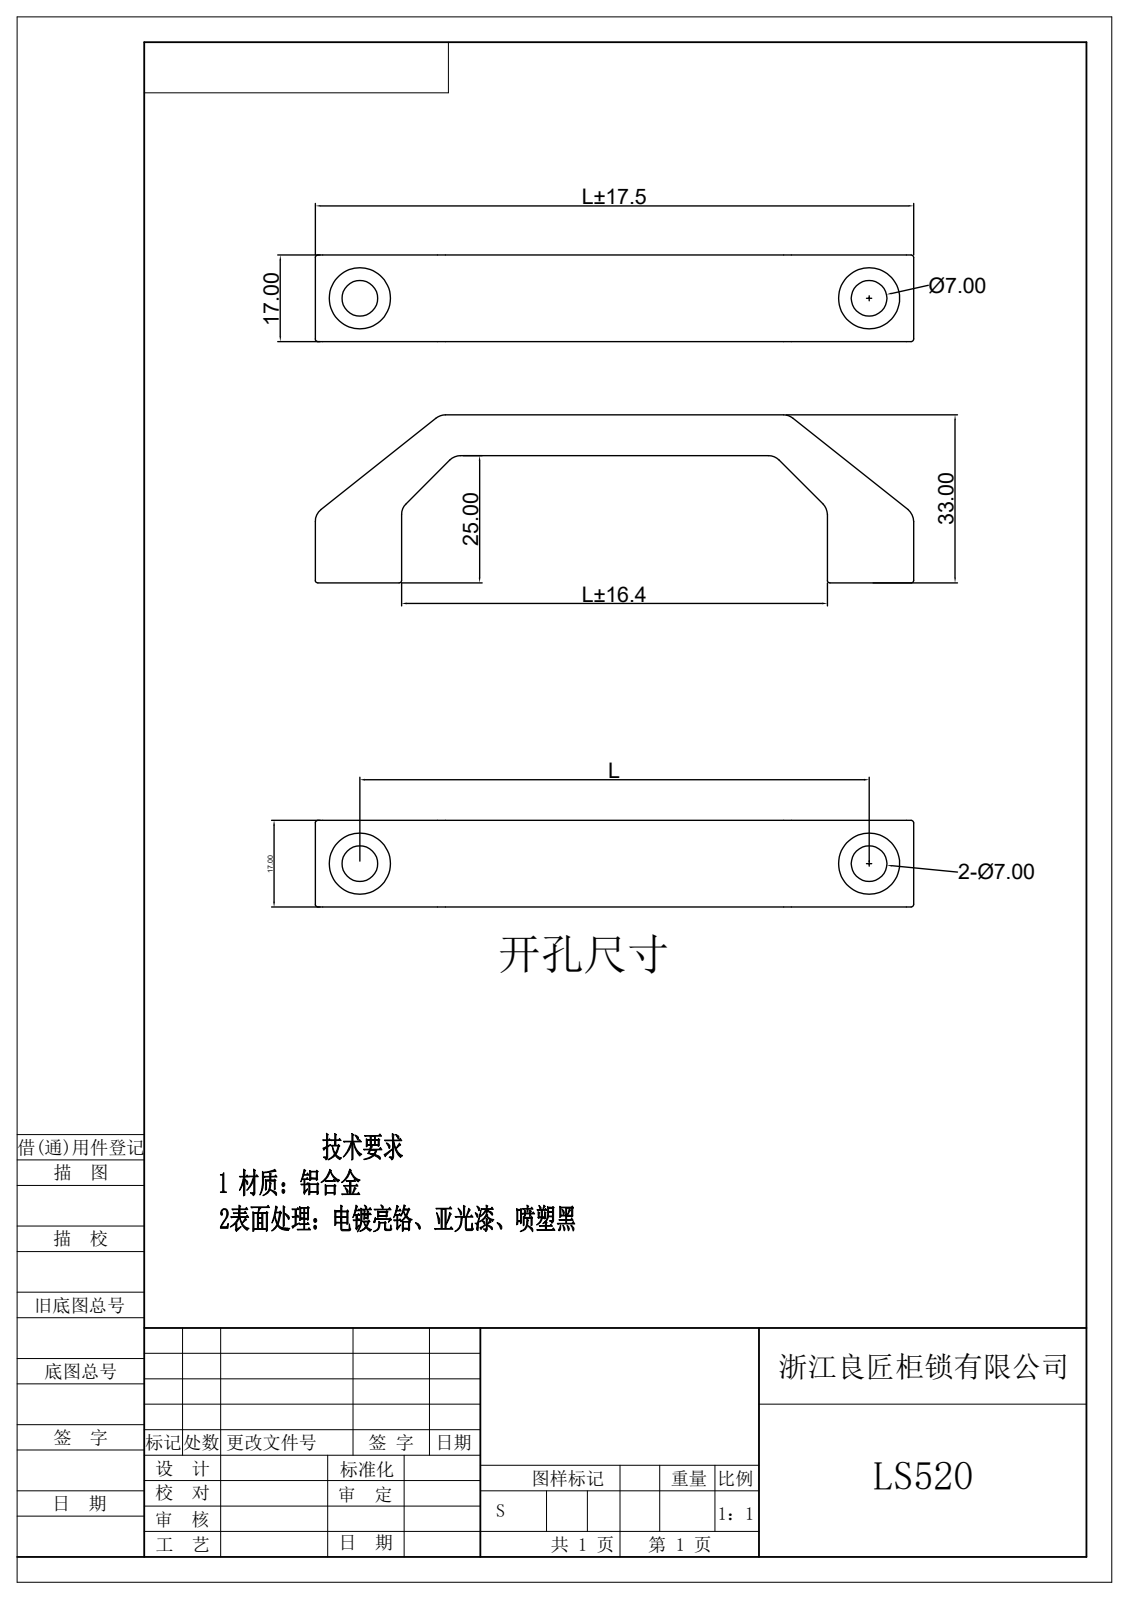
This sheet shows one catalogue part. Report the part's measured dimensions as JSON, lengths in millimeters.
{"step_written_by": "Rhino 8.5 (CONFIG_CONTROL_DESIGN)", "units": "millimeters", "bodies": {"solids": 2, "faces": 172, "planar": 28, "cylindrical": 88, "other": 56}, "overall_size": [147.5, 53.05, 33], "volume_mm3": 43821, "surface_area_mm2": 19774, "round_holes": [[7, 4], [12, 4]], "partial_cylinders_radius": [[0.5, 52], [3, 16]], "face_to_face_distances": [17, 36.05, 8, 53.05, 19.05, 25, 33, 15, 16.95, 115.55], "hole_center_spacings": [39.05, 120.52, 100, 130]}
